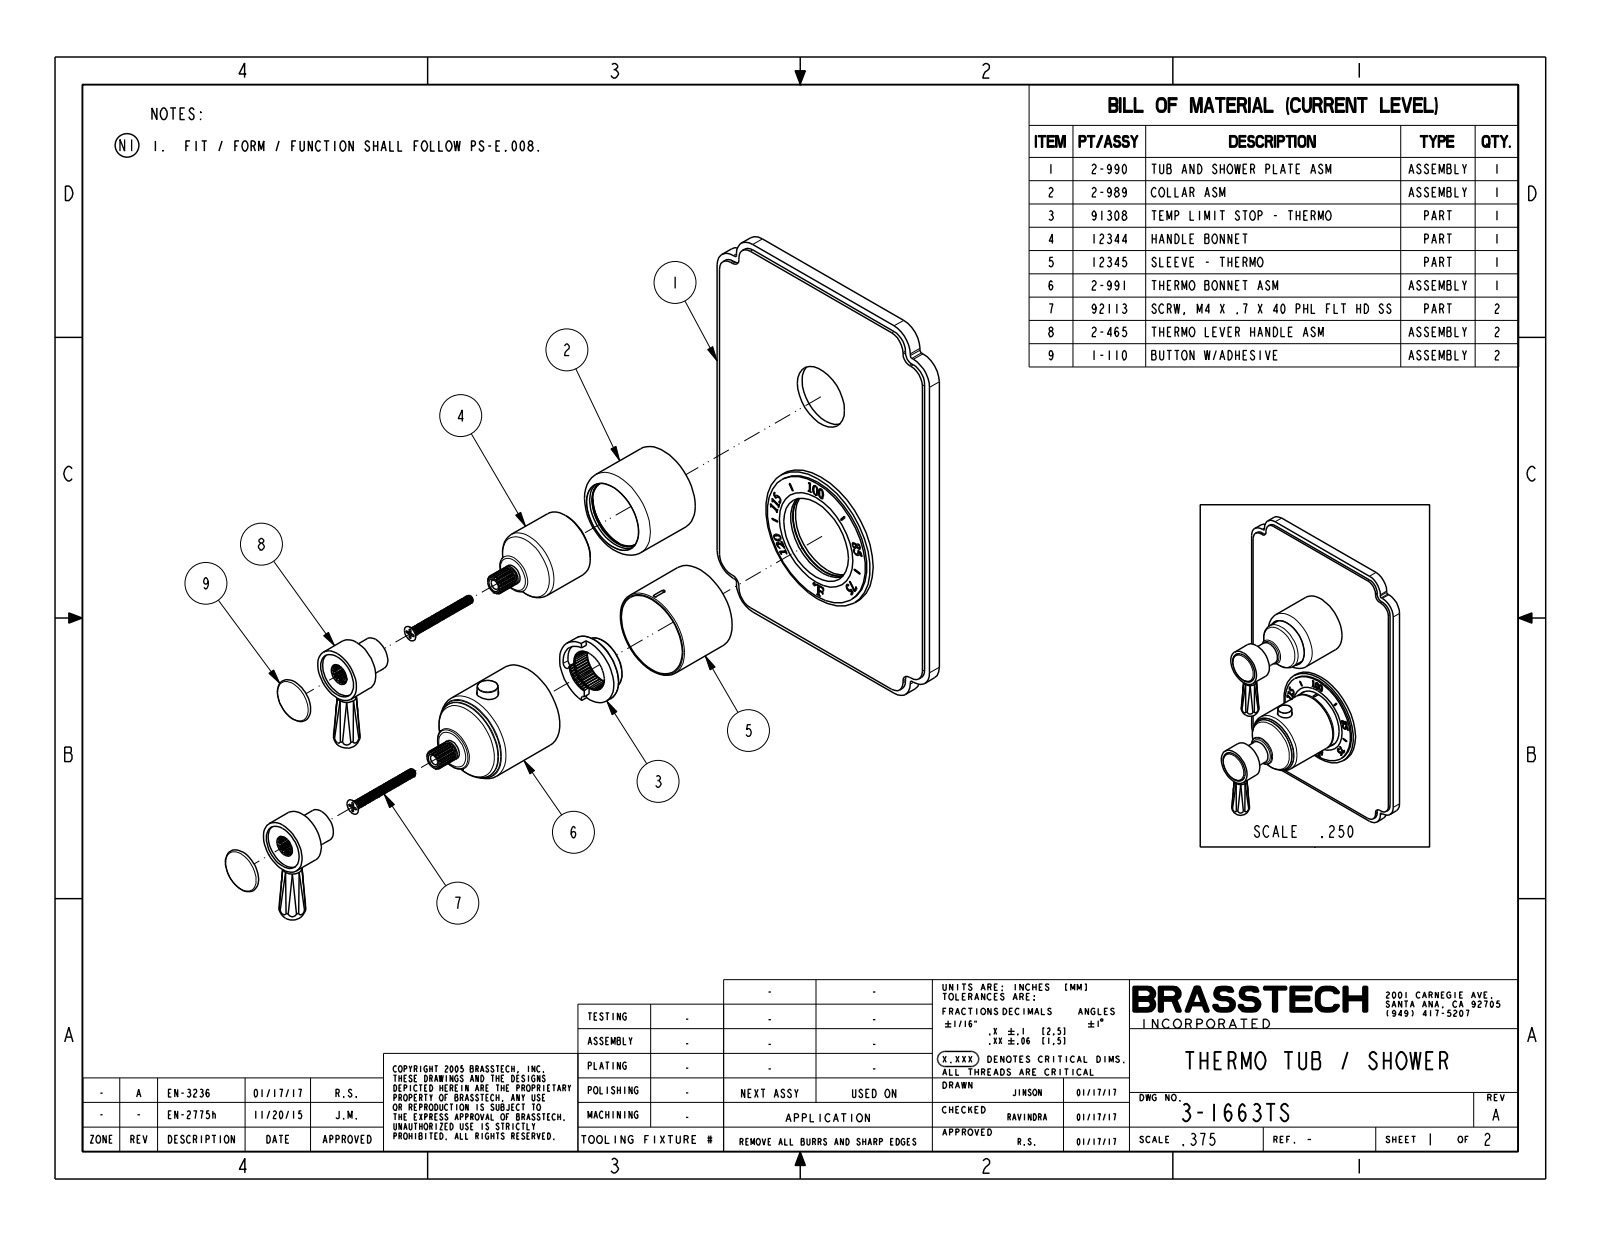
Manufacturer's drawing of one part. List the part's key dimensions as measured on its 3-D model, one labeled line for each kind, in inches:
Part name (STEP PRODUCT): 12343_AF0; H-78_2_FEET_AF0; 91678; 2-990_AF0_ASM (+8 more)
STEP written by: PRO/ENGINEER BY PARAMETRIC TECHNOLOGY CORPORATION, 2013150 (CONFIG_CONTROL_DESIGN)
Units: inches
Bodies: 26 solids, 2327 faces (905 planar, 575 cylindrical, 847 other)
Overall size (bounding box): 8.25 × 5.5 × 4.354
Volume: 10.01 in³ · Surface area: 332.5 in²
Round holes (diameter × count): ⌀0.136 ×4, ⌀0.19 ×2, ⌀0.206 ×2, ⌀0.27 ×2, ⌀0.363 ×2, ⌀0.85 ×2, ⌀0.063 ×1, ⌀0.079 ×1, ⌀0.1 ×1, ⌀0.126 ×1, ⌀0.276 ×1, ⌀0.276 ×1
Round bosses / shafts (diameter × count): ⌀0.164 ×4, ⌀1.654 ×2, ⌀1 ×2, ⌀0.625 ×2, ⌀0.512 ×2, ⌀0.5 ×2, ⌀0.37 ×2, ⌀0.35 ×2
Partial cylindrical surfaces — rounded edges, fillets, slot ends (radius × count): R0.09 ×8, R0.295 ×8, R0.34 ×8, R0.42 ×8, R0.04 ×4, R0.12 ×4, R0.165 ×4, R0.37 ×4
Main face-to-face distances: 0.08, 0.123, 0.043, 0.06, 0.063, 0.25, 0.017, 5.42, 0.233, 0.19
Hole centre spacings: 1.617, 0.367, 0.554, 1.349, 1.716, 2.596, 3.15
